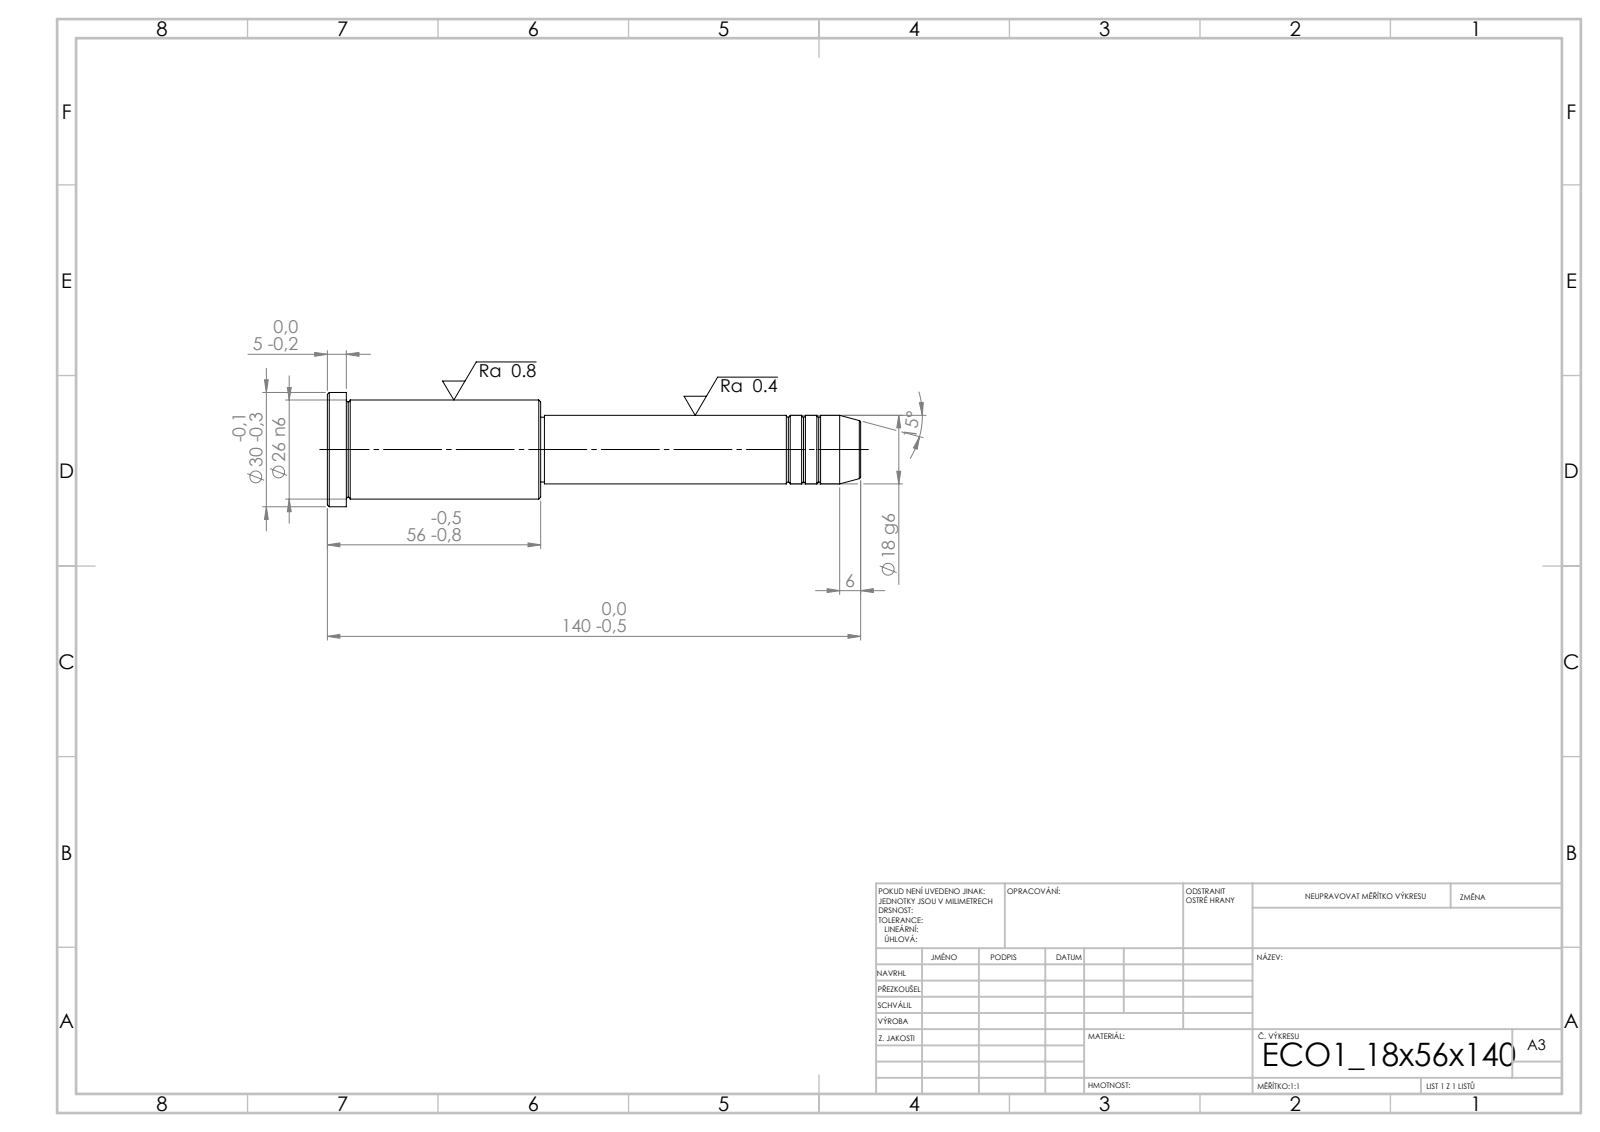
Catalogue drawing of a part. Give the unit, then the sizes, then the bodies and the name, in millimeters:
Units: millimetres
Overall size (bounding box): 140 × 30 × 30
Round bosses / shafts (diameter × count): ⌀30 ×1, ⌀26 ×1, ⌀18 ×1, ⌀17 ×1
Main face-to-face distances: 56, 51, 5, 84, 135, 140, 83, 1, 52, 57
Volume: 51 623 mm³ · Surface area: 10 834 mm²
Bodies: 1 solid, 43 faces (5 planar, 14 cylindrical, 24 other)
STEP written by: SolidWorks 2019 (CONFIG_CONTROL_DESIGN)
